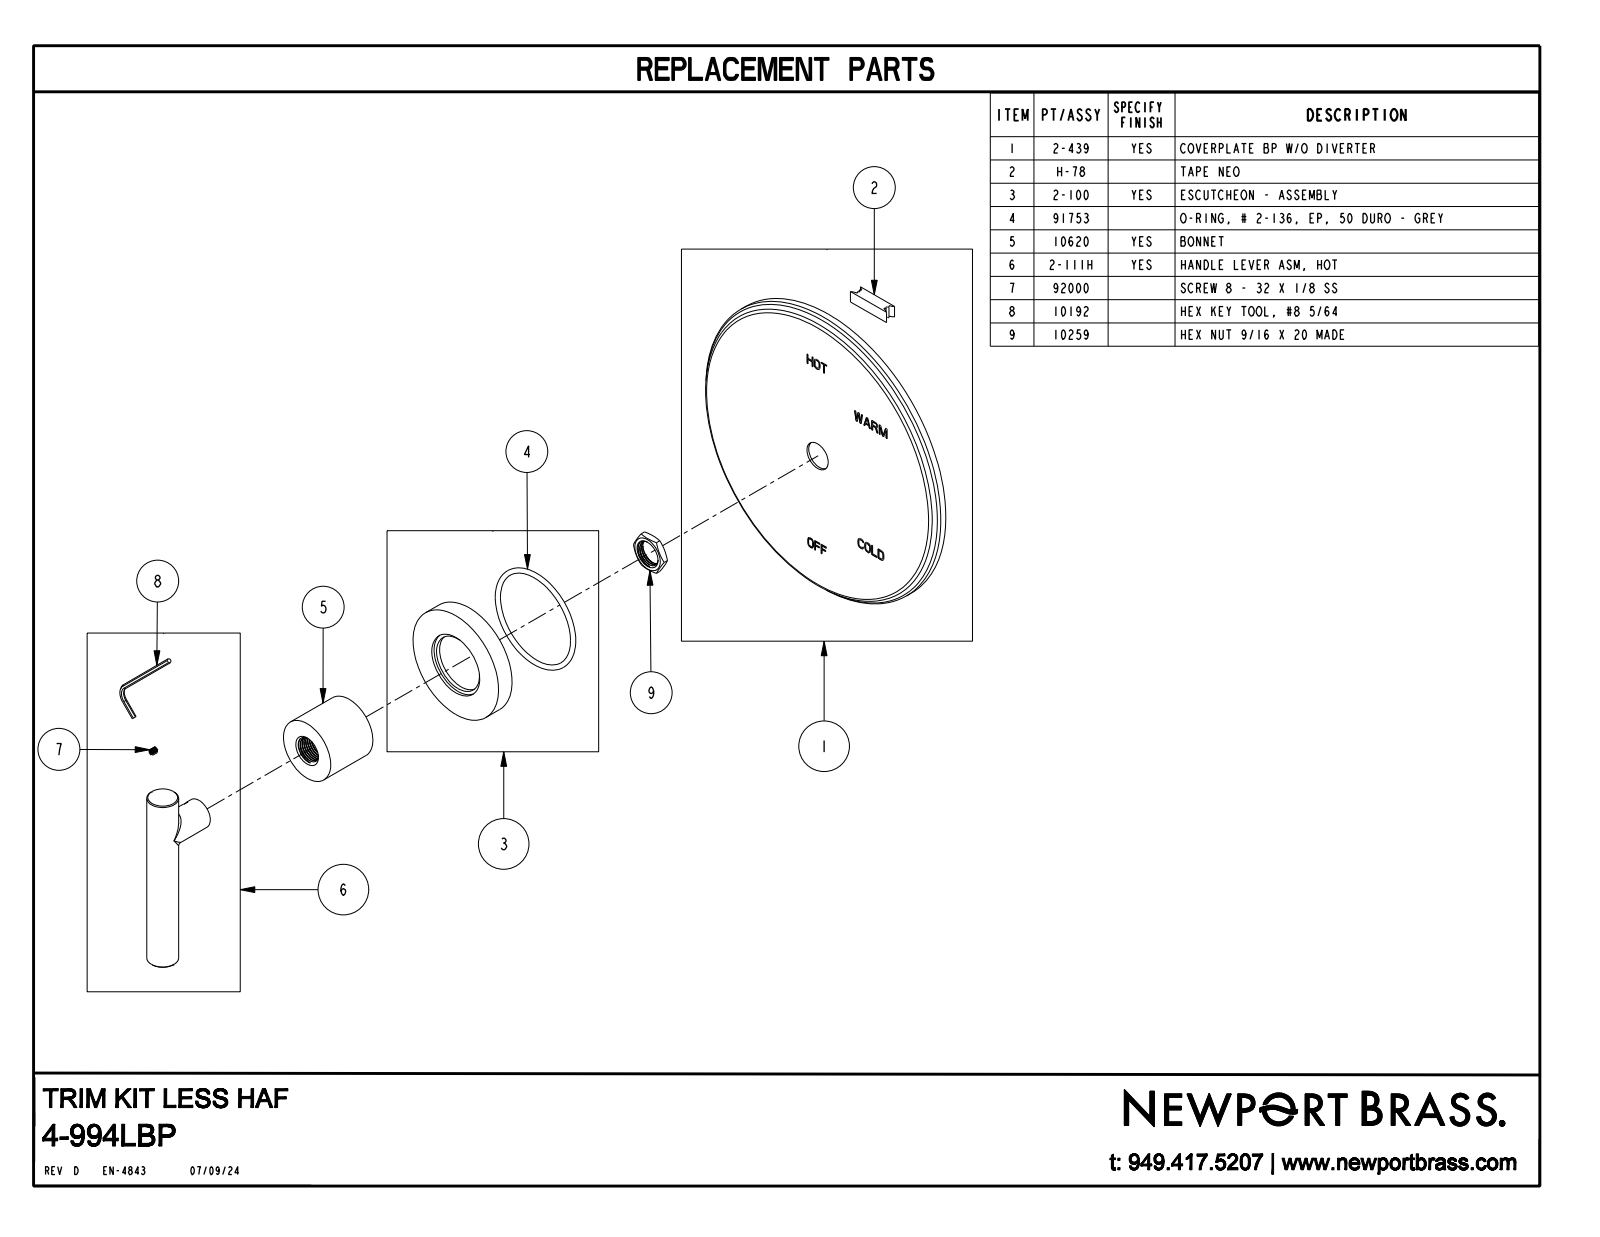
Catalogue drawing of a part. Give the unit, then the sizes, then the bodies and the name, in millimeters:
Units: millimetres
Overall size (bounding box): 165.1 × 165.1 × 79.7
Round bosses / shafts (diameter × count): ⌀15.9 ×2, ⌀165.1 ×1, ⌀60.3 ×1, ⌀33.4 ×1, ⌀10.2 ×1
Main face-to-face distances: 8, 17.5, 9.5, 45.6, 37.7, 28.1, 98.4, 0.5, 38.2, 46.1
Volume: 241 400 mm³ · Surface area: 56 700 mm²
Bodies: 1 solid, 361 faces (334 planar, 13 cylindrical, 14 other)
Part name (STEP PRODUCT): 4-994LBP
STEP written by: CREO PARAMETRIC BY PTC INC, 2018400 (CONFIG_CONTROL_DESIGN)
